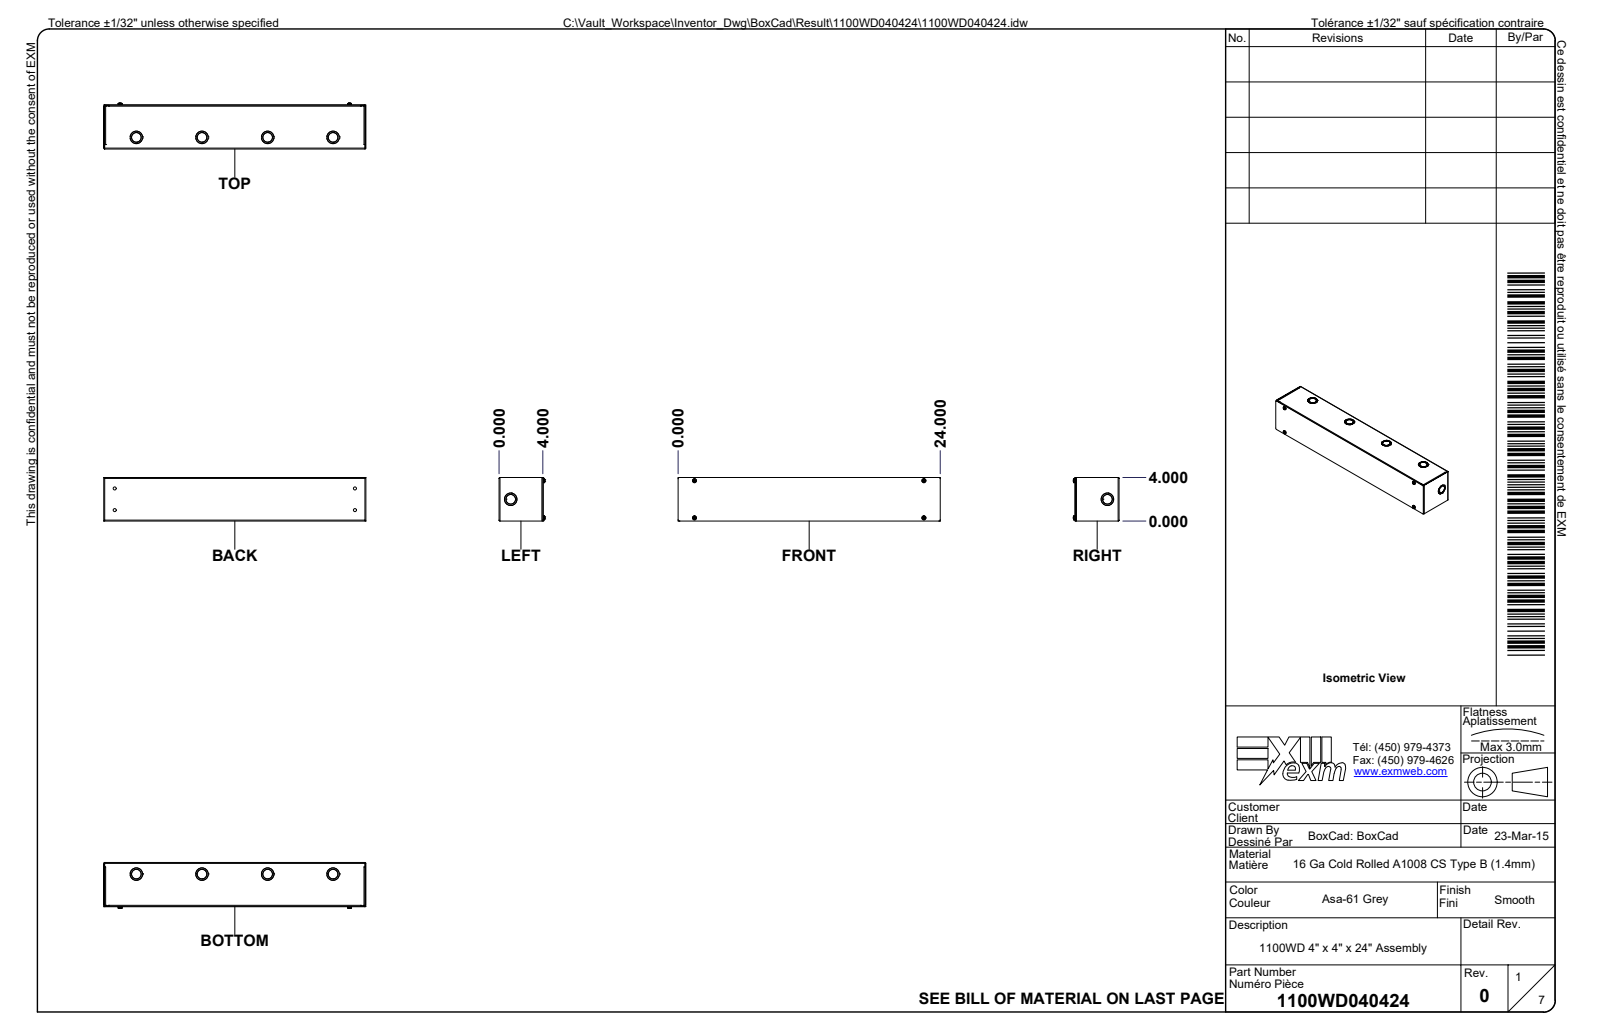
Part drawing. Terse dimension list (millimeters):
name: 1100WD040424; 1100WD040424B; 1100WD040424B-P; 1100WD040424C (+5 more)
written by: Autodesk Inventor 2024 (AUTOMOTIVE_DESIGN)
unit: mm
bodies: 8 solids, 3382 faces (2063 planar, 427 cylindrical, 892 other)
size: 609.6 × 106.2 × 101.6
volume: 394 800 mm³; area: 581 900 mm²
holes: 8× ⌀7.4, 5× ⌀22.2, 5× ⌀28.6, 4× ⌀4.2, 2× ⌀0.8, 2× ⌀4.5, 1× ⌀1.1, 1× ⌀7.9, 1× ⌀27
bosses: 5× ⌀28.6, 5× ⌀22.2, 4× ⌀9.5, 2× ⌀0.8, 1× ⌀31.8, 1× ⌀29, 1× ⌀6.4, 1× ⌀1.3
rounds: 28× R0.1, 14× R0.8, 14× R2.2, 12× R1.5, 12× R2.8, 4× R1.6, 4× R2.4, 4× R3.2
face distances: 1.4, 100.2, 101.6, 98.8, 1.3, 101.5, 102.9, 608.2, 2.7, 609.6
hole spacings: 21.8, 69.7, 546.4, 550.4, 152.4, 50.8, 78.6, 86.4
